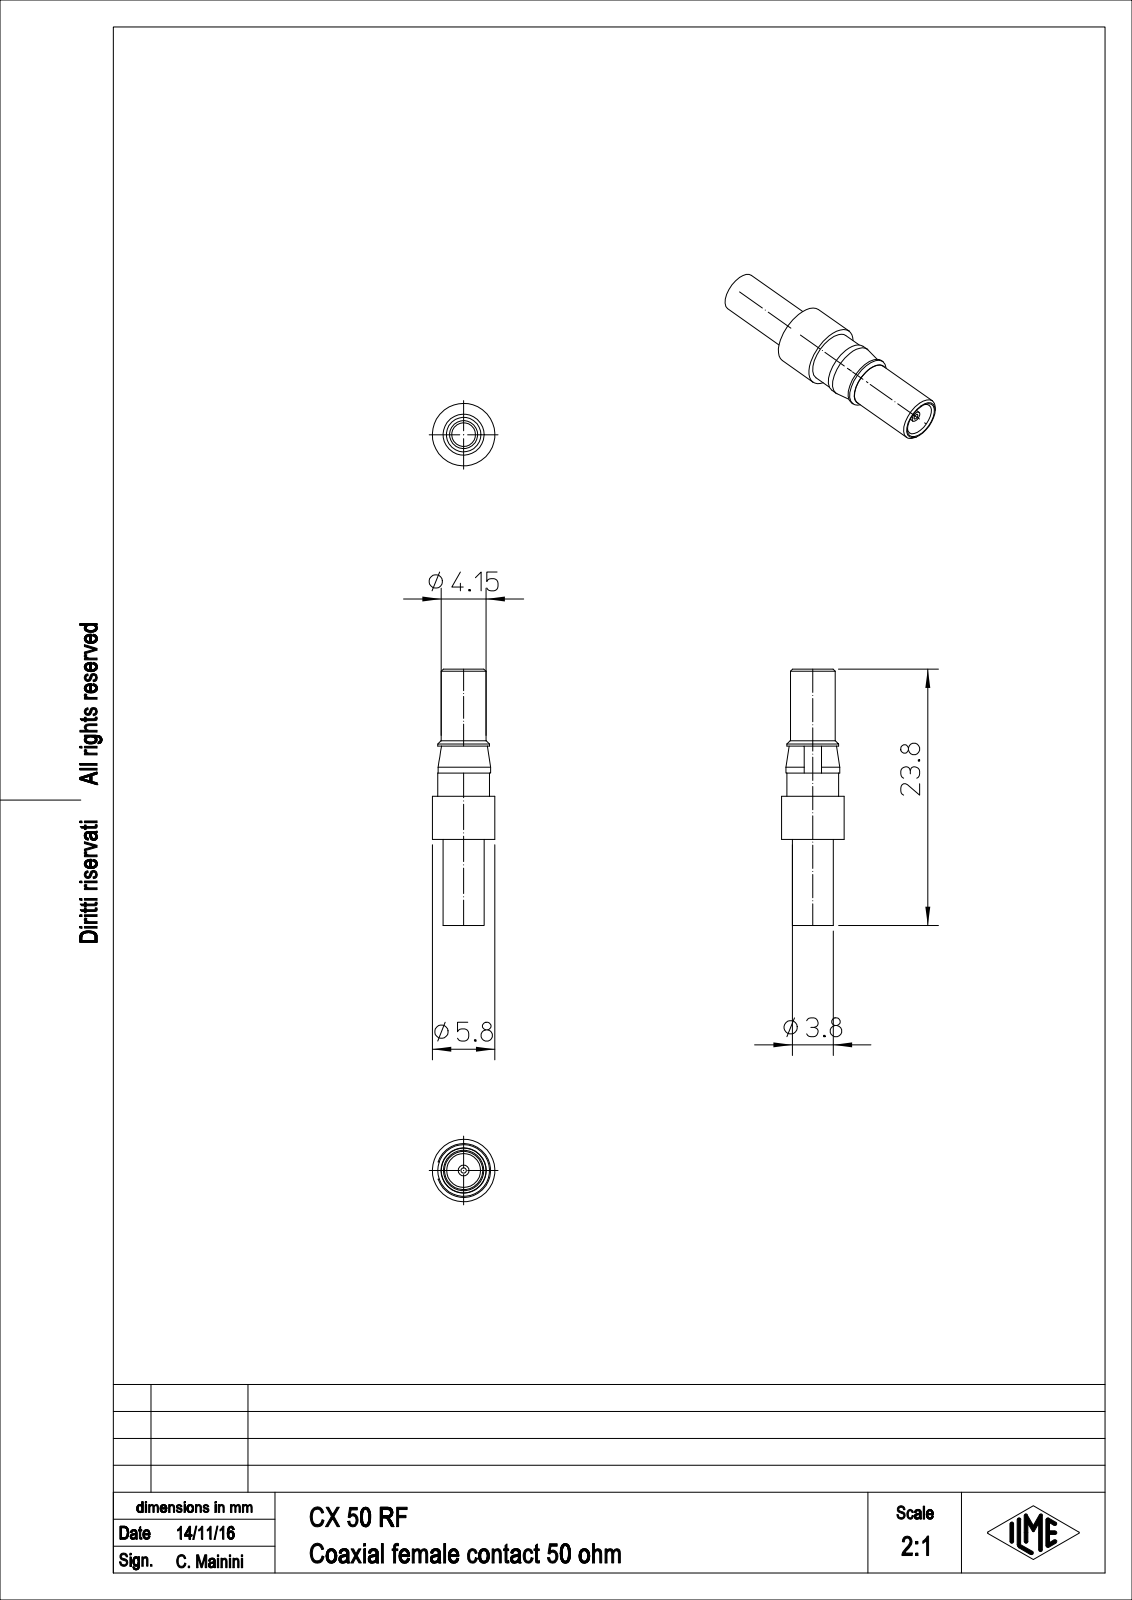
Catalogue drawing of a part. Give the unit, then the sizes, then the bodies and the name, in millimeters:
Units: millimetres
Overall size (bounding box): 23.8 × 5.8 × 5.8
Round holes (diameter × count): ⌀0.5 ×1, ⌀2.2 ×1, ⌀3.15 ×1, ⌀3.2 ×1
Round bosses / shafts (diameter × count): ⌀5.8 ×1, ⌀5 ×1, ⌀4.8 ×1, ⌀4.15 ×1, ⌀3.8 ×1, ⌀2.6 ×1, ⌀1 ×1
Partial cylindrical surfaces — rounded edges, fillets, slot ends (radius × count): R1.75 ×1
Main face-to-face distances: 4, 5.45, 9.45, 0.8, 4.65, 8.65, 17.45, 16.65, 12, 8
Volume: 257 mm³ · Surface area: 663 mm²
Bodies: 1 solid, 47 faces (16 planar, 24 cylindrical, 7 other)
Part name (STEP PRODUCT): CX_50_RF
STEP written by: PTC Creo Elements/Direct Modeling 19.0E 27-Jun-2016 (C) Parametric Technology GmbH (AUTOMOTIVE_DESIGN)
